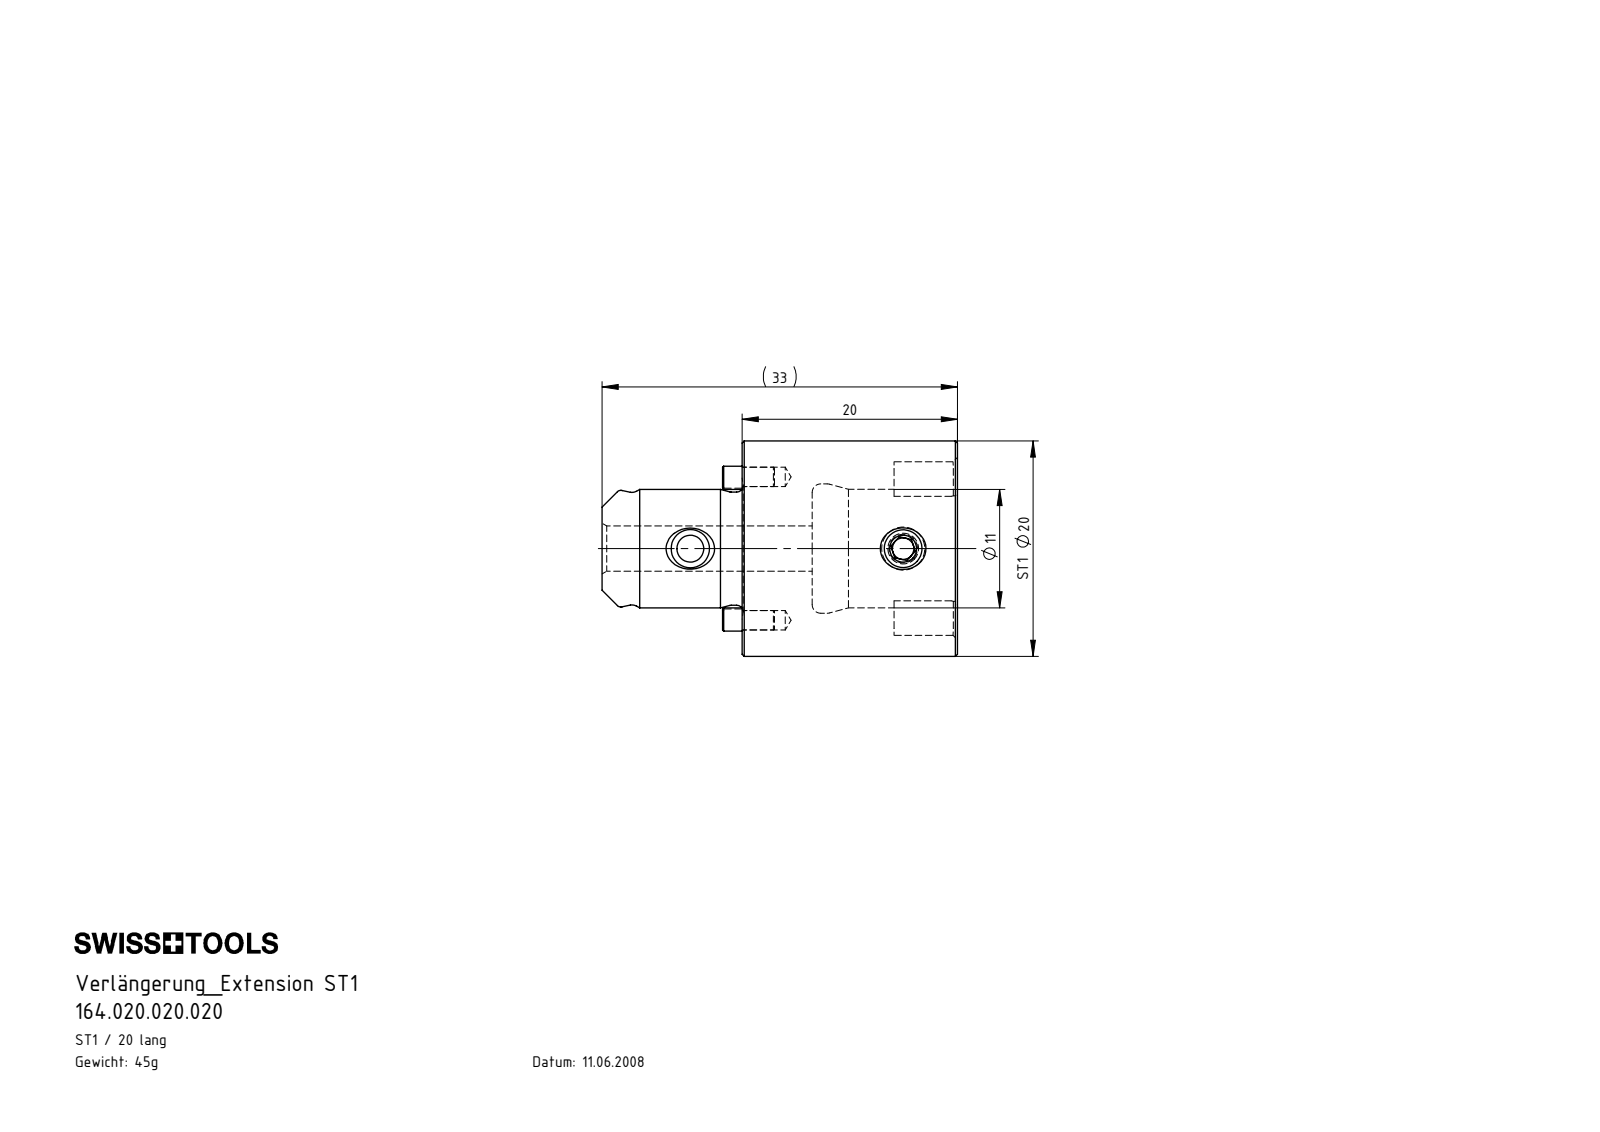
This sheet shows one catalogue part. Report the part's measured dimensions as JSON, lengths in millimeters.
{"part_name": "ST1-ER2.001.005_A; ST1-ST1.K01.020; ST1-ER1.001.005_A; ST1-ST1.K01.020_A", "step_written_by": "SolidWorks 2015 (CONFIG_CONTROL_DESIGN)", "units": "millimeters", "bodies": {"solids": 4, "faces": 146, "planar": 26, "cylindrical": 43, "other": 77}, "overall_size": [33, 20, 20], "volume_mm3": 5745, "surface_area_mm2": 3284, "round_holes": [[1.8, 2], [2.5, 1], [3.5, 1], [4.2, 1], [11, 1], [12, 1]], "round_bosses_or_shafts": [[20, 1], [10.8, 1], [10.5, 1], [4, 1]], "partial_cylinders_radius": [[0.3, 4], [1.3, 2], [1.48, 2], [5.55, 2]], "face_to_face_distances": [20, 6.5, 13.5, 9.34, 13, 19.5, 33, 27.1, 14.1, 7.6], "hole_center_spacings": [6.65, 13.3, 19.75]}
